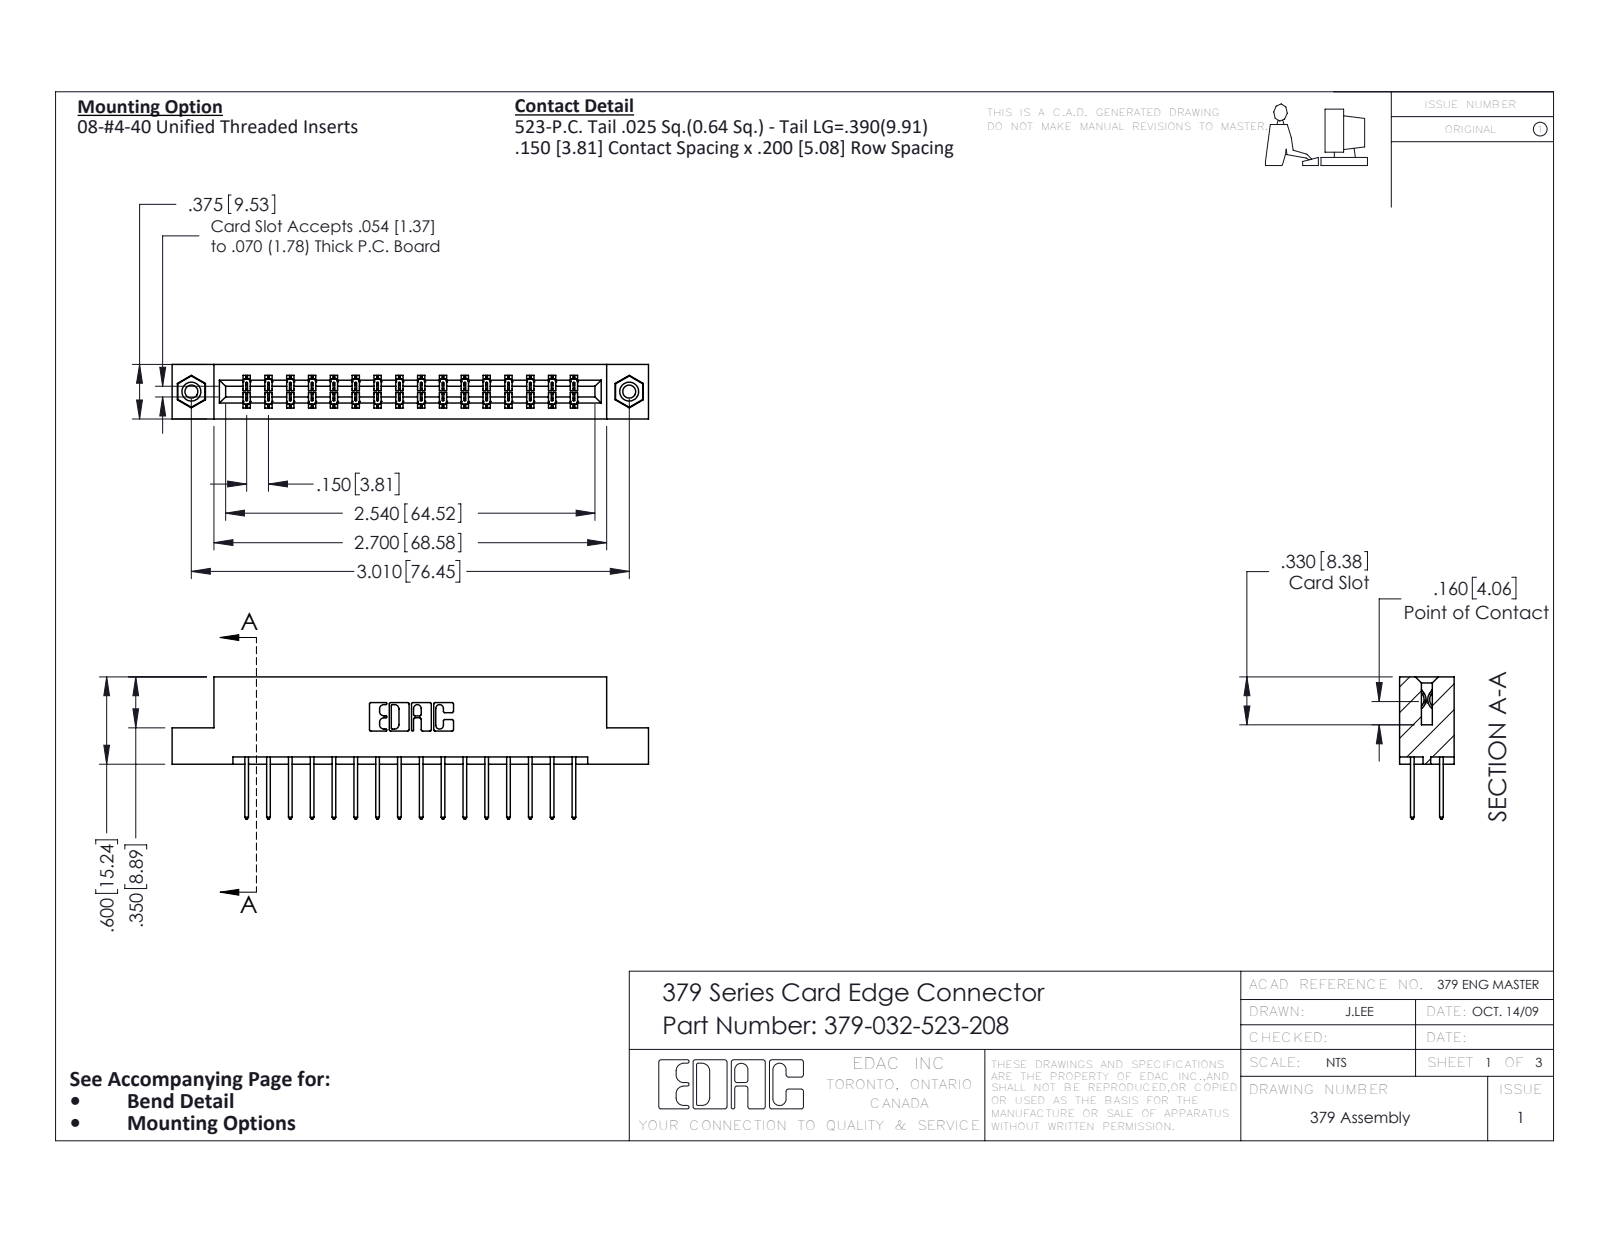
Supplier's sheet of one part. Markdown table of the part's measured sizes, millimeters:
| quantity | value |
| --- | --- |
| part name | 345-250-001_345-250-003-102; 379-032-523-208; 345-292-001_345-293-123; 379 Part_Flush - .156 Dia - TI |
| STEP written by | SolidWorks 2020 (CONFIG_CONTROL_DESIGN) |
| units | millimeters |
| bodies | 35 solids, 1838 faces (1254 planar, 568 cylindrical, 16 other) |
| overall size | 83.2 × 24.8 × 9.5 |
| volume | 8 590 mm³ |
| surface area | 9 748 mm² |
| round holes (diameter × count) | 2.3 × 2, 3.2 × 2, 4 × 2 |
| round bosses / shafts (diameter × count) | 3.9 × 2 |
| partial cylindrical surfaces (radius × count) | 0.2 × 63, 0.3 × 32, 0.3 × 22, 0.2 × 6, 0.8 × 6, 0.7 × 3, 0.4 × 2, 0.6 × 2 |
| main face-to-face distances | 7.6, 1.9, 5.1, 9.5, 2.5, 3.8, 1.3, 15.2, 5.7, 7 |
| hole center spacings | 76.5 |
